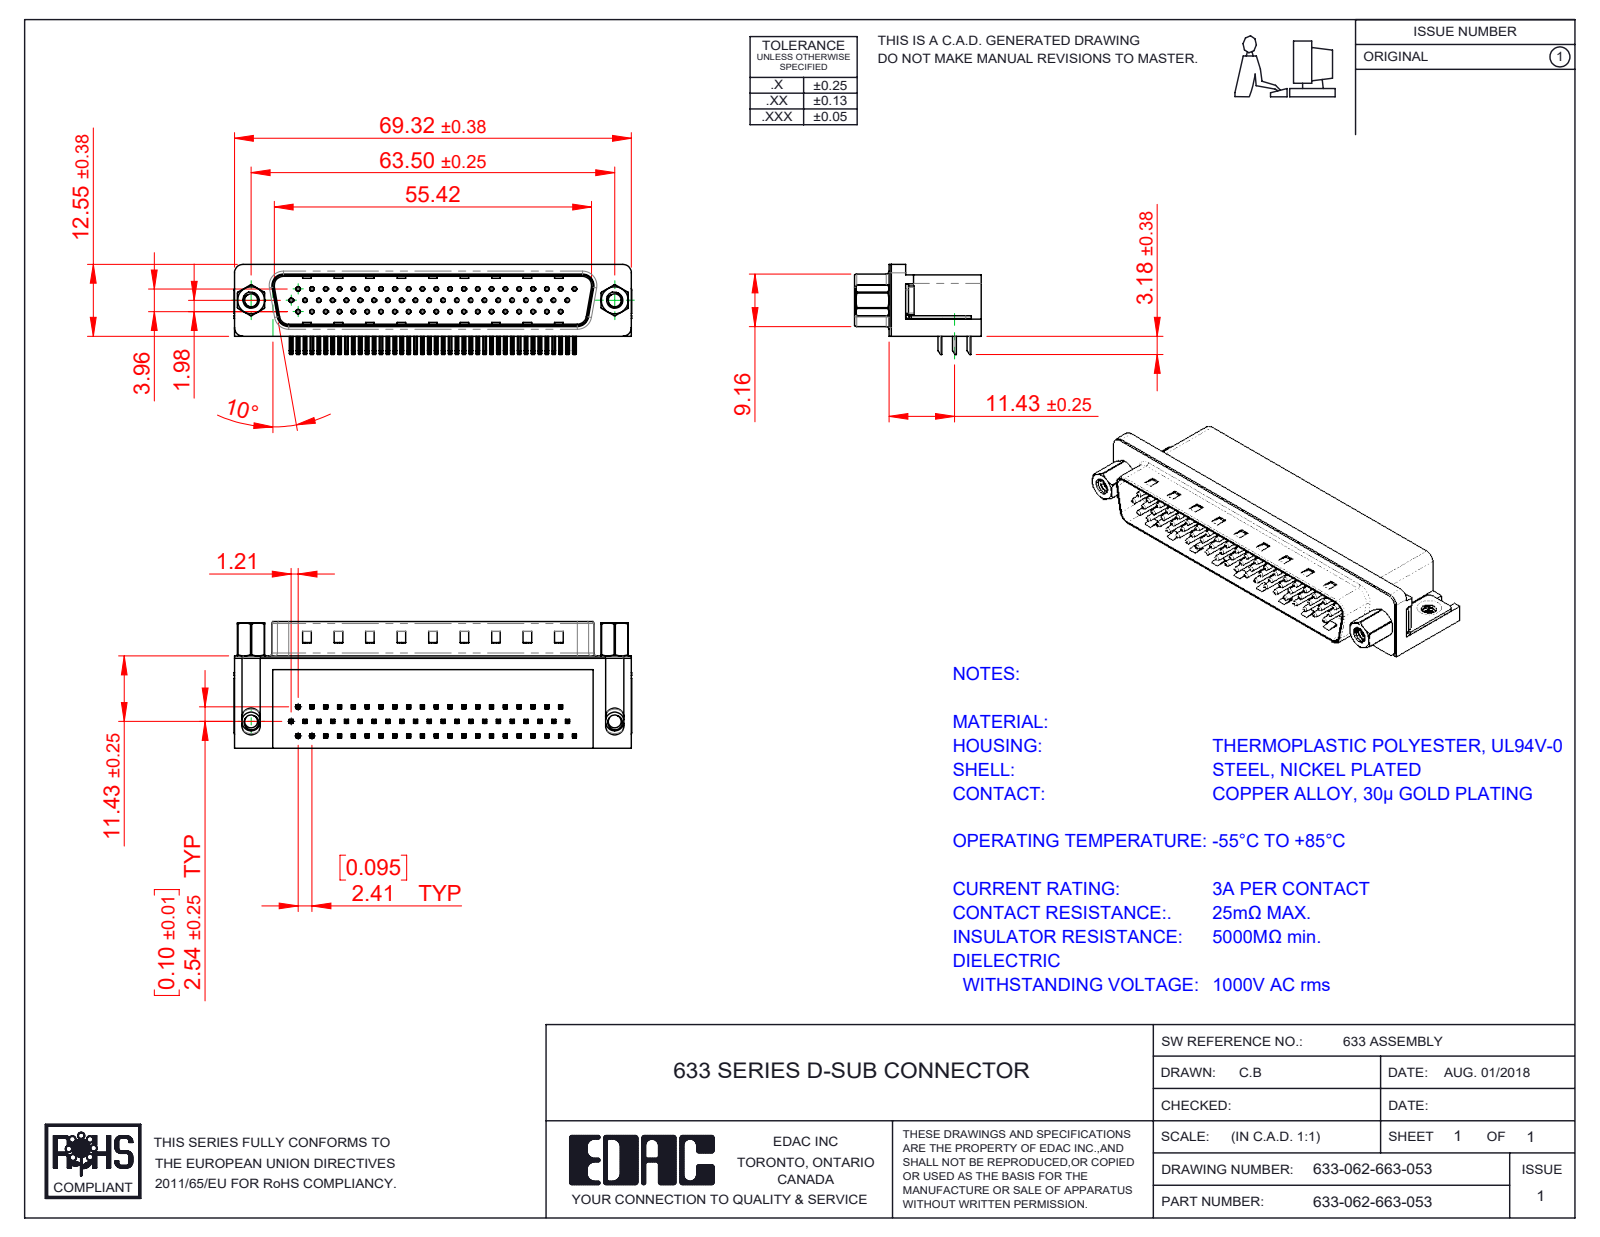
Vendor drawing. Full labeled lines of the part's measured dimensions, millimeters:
Part name (STEP PRODUCT): 633 Housing_62 Contact; 633 Shell_62 Contact; 633 4-40 Threaded Board Mount; 633 4-40 Hex Standoff (+5 more)
STEP written by: SolidWorks 2016 (CONFIG_CONTROL_DESIGN)
Units: millimetres
Bodies: 70 solids, 5226 faces (3235 planar, 1518 cylindrical, 473 other)
Overall size (bounding box): 69.4 × 22.1 × 15.73
Volume: 11 269 mm³ · Surface area: 13 938 mm²
Round holes (diameter × count): ⌀0.35 ×62, ⌀0.8 ×62, ⌀2.26 ×4, ⌀2.29 ×2, ⌀4 ×2, ⌀4.8 ×2, ⌀5 ×2
Round bosses / shafts (diameter × count): ⌀0.75 ×62, ⌀4.9 ×2, ⌀4.75 ×2, ⌀3.9 ×2, ⌀3.26 ×2, ⌀2.79 ×2
Partial cylindrical surfaces — rounded edges, fillets, slot ends (radius × count): R0.25 ×256, R0.12 ×124, R1 ×16, R0.5 ×9, R1.6 ×8, R1.5 ×7, R0.9 ×4, R2 ×4
Main face-to-face distances: 0.4, 10.35, 15.7, 8.76, 2.9, 2.5, 2.54, 8.36, 16.1, 2.1
Hole centre spacings: 2.41, 4.82, 7.24, 9.65, 14.48, 16.89, 4.83, 7.23
